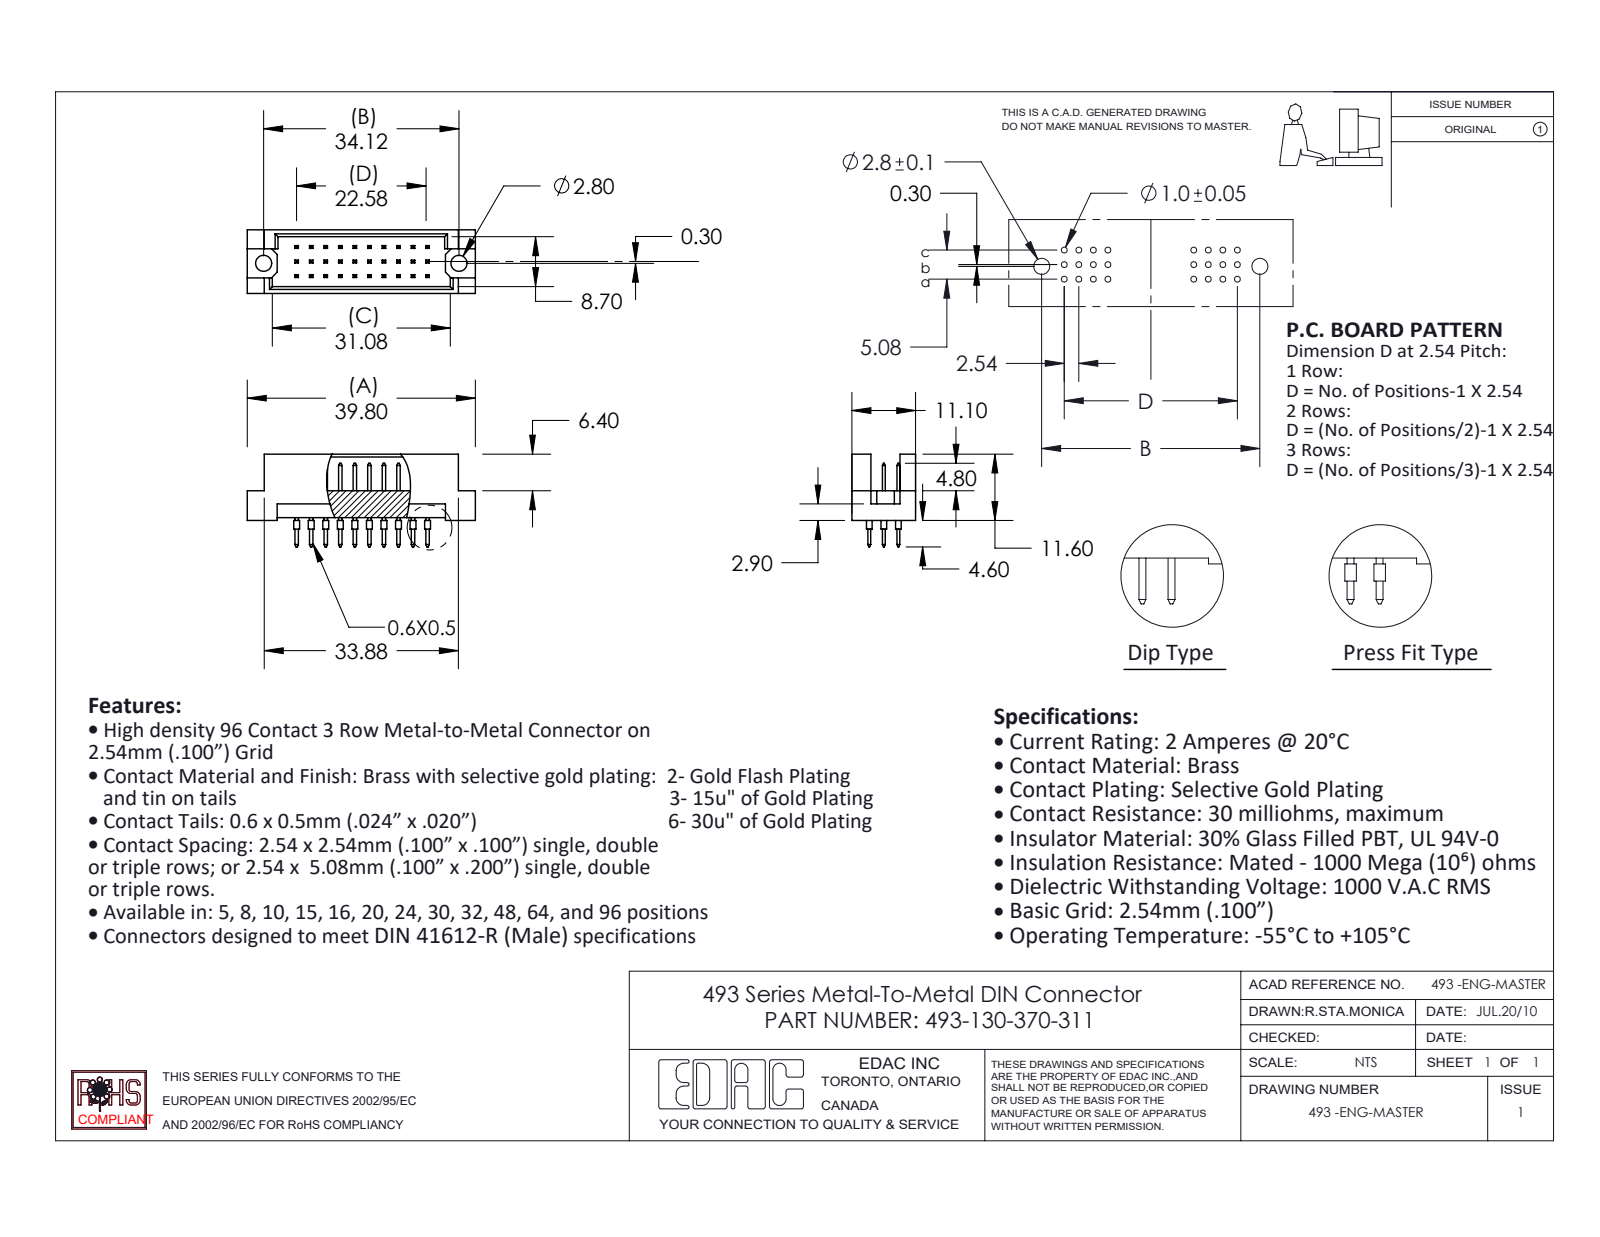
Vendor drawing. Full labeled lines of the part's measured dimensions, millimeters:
Part name (STEP PRODUCT): 493-290_70; 493-130-370-311; 493 Part_30
STEP written by: SolidWorks 2020 (CONFIG_CONTROL_DESIGN)
Units: millimetres
Bodies: 31 solids, 832 faces (768 planar, 64 cylindrical, 0 other)
Overall size (bounding box): 39.8 × 16.2 × 11.1
Volume: 2 523 mm³ · Surface area: 3 761 mm²
Round holes (diameter × count): ⌀2.8 ×2
Round bosses / shafts (diameter × count): ⌀1 ×30
Main face-to-face distances: 2.54, 5.08, 1.2, 9.9, 0.5, 11.1, 8.7, 7.62, 4.7, 4.6
Hole centre spacings: 34.12
